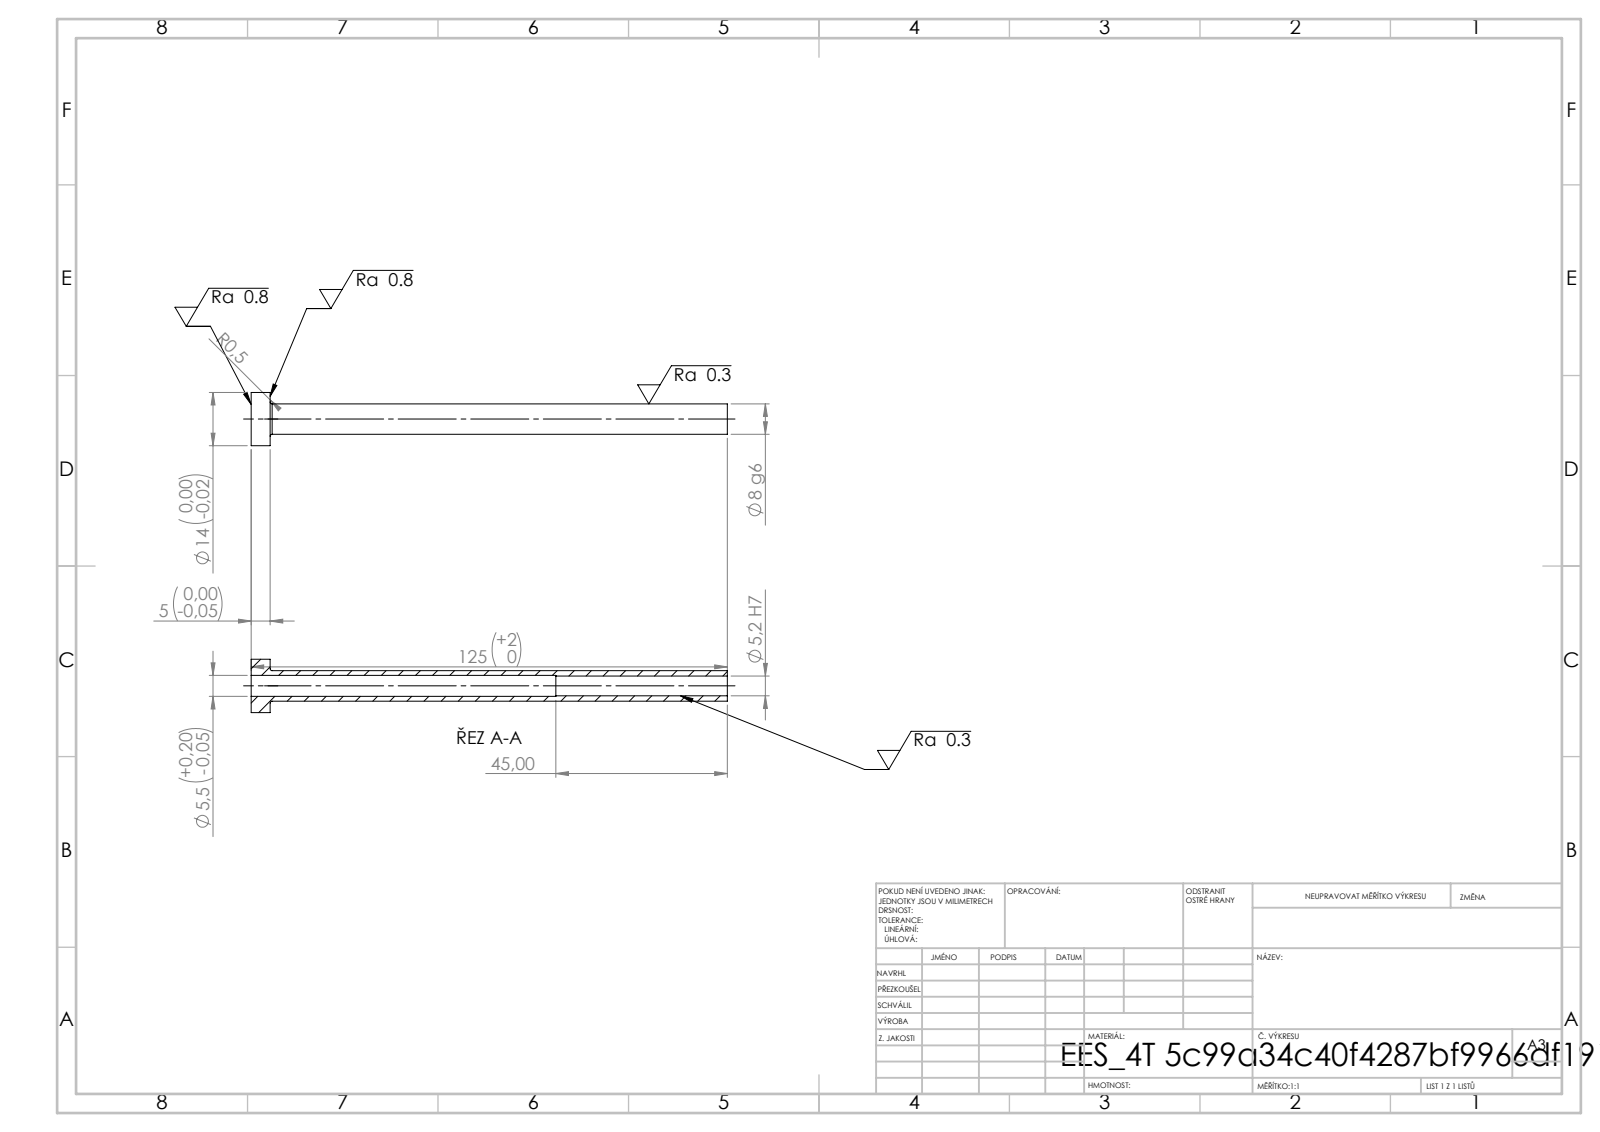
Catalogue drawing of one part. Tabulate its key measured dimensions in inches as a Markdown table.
| quantity | value |
| --- | --- |
| STEP written by | SolidWorks 2019 (CONFIG_CONTROL_DESIGN) |
| units | inches |
| bodies | 1 solid, 14 faces (4 planar, 8 cylindrical, 2 other) |
| overall size | 4.921 × 0.551 × 0.551 |
| volume | 0.241 in³ |
| surface area | 8.7 in² |
| round holes (diameter × count) | 0.205 × 1, 0.217 × 1 |
| round bosses / shafts (diameter × count) | 0.551 × 1, 0.315 × 1 |
| main face-to-face distances | 0.197, 4.921, 4.724, 3.15, 2.953, 1.772 |
